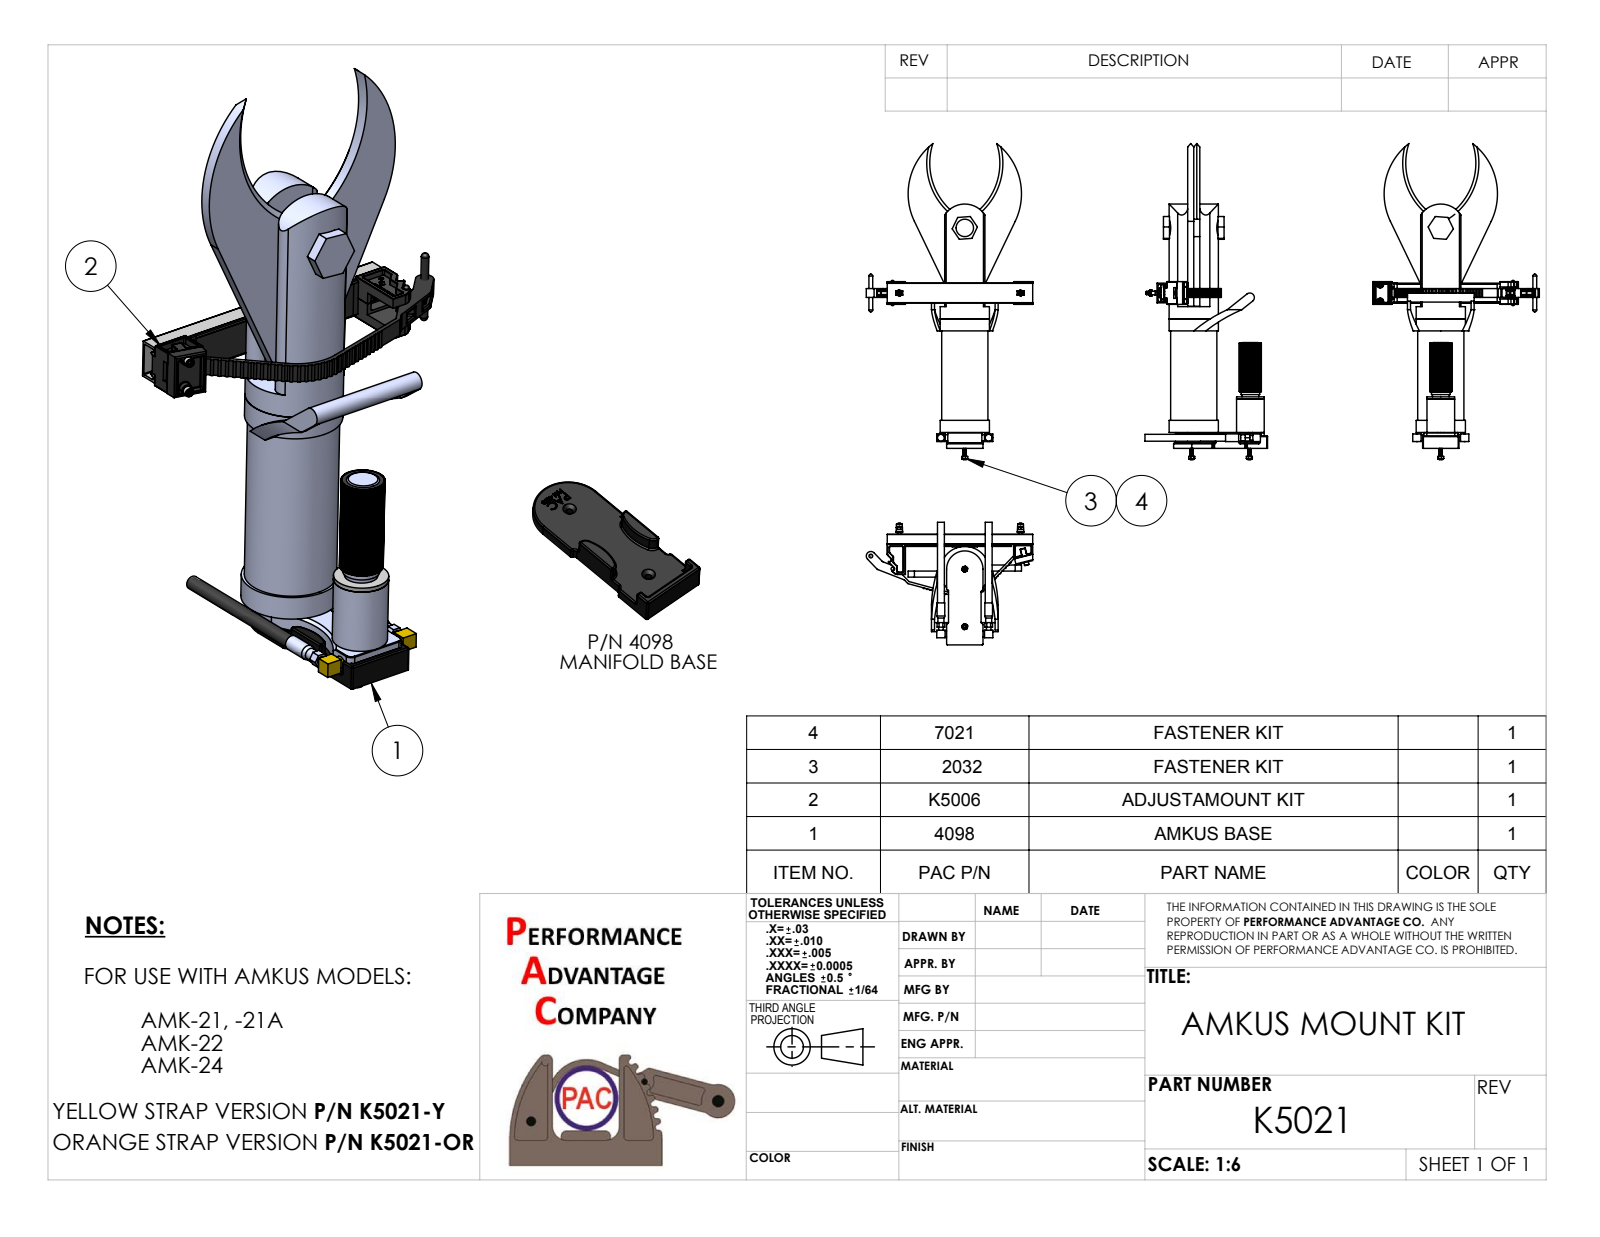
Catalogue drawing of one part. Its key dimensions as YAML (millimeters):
part_name: "K5021; 2031_CR-FHMS 0.25-20x0.75x0.75-N; 2011; 2035 Pack_10\" apart (+8 more)"
step_written_by: "SolidWorks 2010 (CONFIG_CONTROL_DESIGN)"
units: millimeters
bodies: {solids: 41, faces: 1912, planar: 891, cylindrical: 575, other: 446}
overall_size: [661.9, 348.7, 256.8]
volume: 5072000
surface_area: 678700
round_holes:
  - {diameter: 5.1, count: 8}
  - {diameter: 6.4, count: 6}
  - {diameter: 6.8, count: 4}
  - {diameter: 6.8, count: 2}
  - {diameter: 7.3, count: 2}
  - {diameter: 8, count: 2}
  - {diameter: 6.6, count: 1}
  - {diameter: 7.4, count: 1}
  - {diameter: 15.9, count: 1}
  - {diameter: 16.3, count: 1}
round_bosses_or_shafts:
  - {diameter: 9.5, count: 6}
  - {diameter: 6.4, count: 5}
  - {diameter: 10.3, count: 4}
  - {diameter: 16.1, count: 2}
  - {diameter: 15.9, count: 2}
  - {diameter: 14.4, count: 2}
  - {diameter: 12.6, count: 2}
  - {diameter: 11.5, count: 2}
partial_cylinders:
  - {radius: 1.6, count: 91}
  - {radius: 1.6, count: 49}
  - {radius: 0.8, count: 35}
  - {radius: 0.5, count: 30}
  - {radius: 1.5, count: 8}
  - {radius: 6.4, count: 6}
  - {radius: 2.4, count: 4}
  - {radius: 3.2, count: 4}
face_to_face_distances: [12.7, 25.4, 4.8, 271.4, 69.1, 56.4, 43.7, 33.4, 64.3, 51.6]
hole_center_spacings: [5.4, 6.4, 34.9, 120.7, 254, 259.4, 260.4, 265.8]
